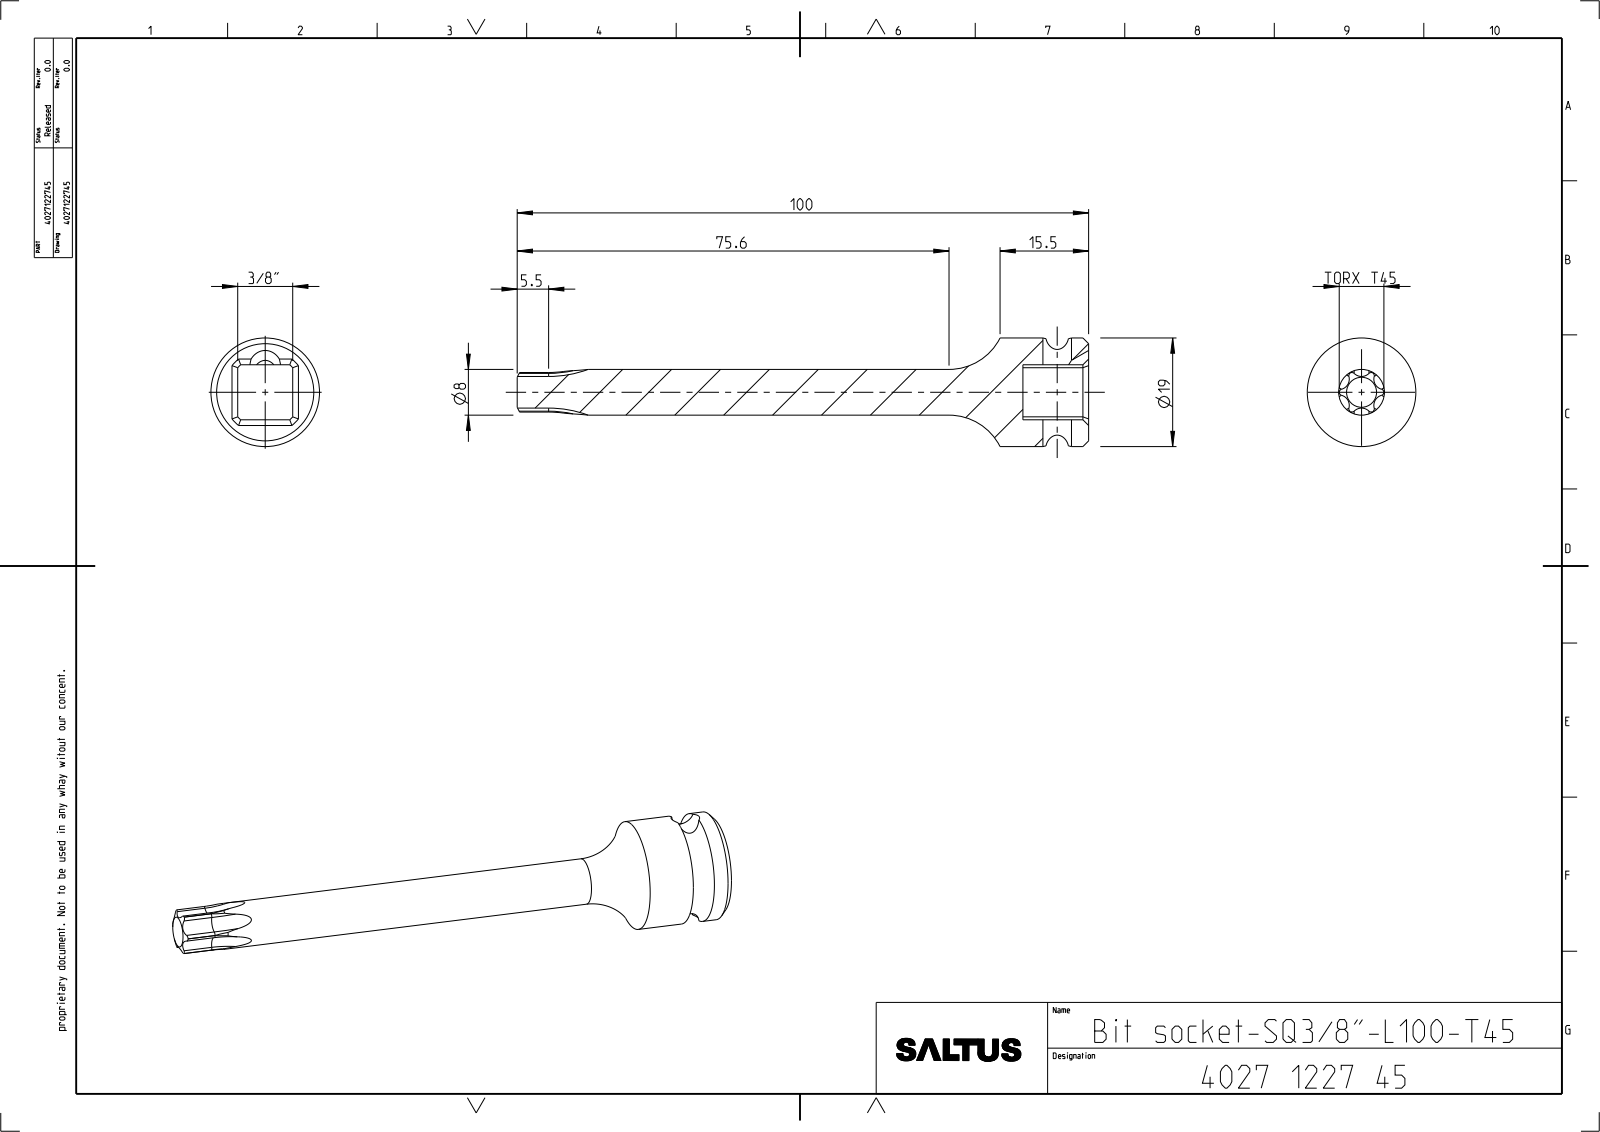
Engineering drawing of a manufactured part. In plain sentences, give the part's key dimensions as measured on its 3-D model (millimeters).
The part is named "4027122745". Its 3-D file was written by "CREO PARAMETRIC BY PTC INC, 2022414 (CONFIG_CONTROL_DESIGN)". It is 1 solid with 87 faces: 12 planar, 39 cylindrical and 36 other. Overall it measures 100 by 19 by 19 millimeters. Its volume is 7 441 cubic millimeters and its surface area 4 015 square millimeters. Round holes: 1 of diameter 5. Round bosses or shafts: 1 of diameter 19, 1 of diameter 8. Partial cylindrical surfaces (rounded edges, fillets, slot ends): 12 of radius 0.54, 6 of radius 1.83, 1 of radius 3, 1 of radius 3.91, 1 of radius 6.45. The main face-to-face distances are 9.62, 11.5, 100, 88.5.
